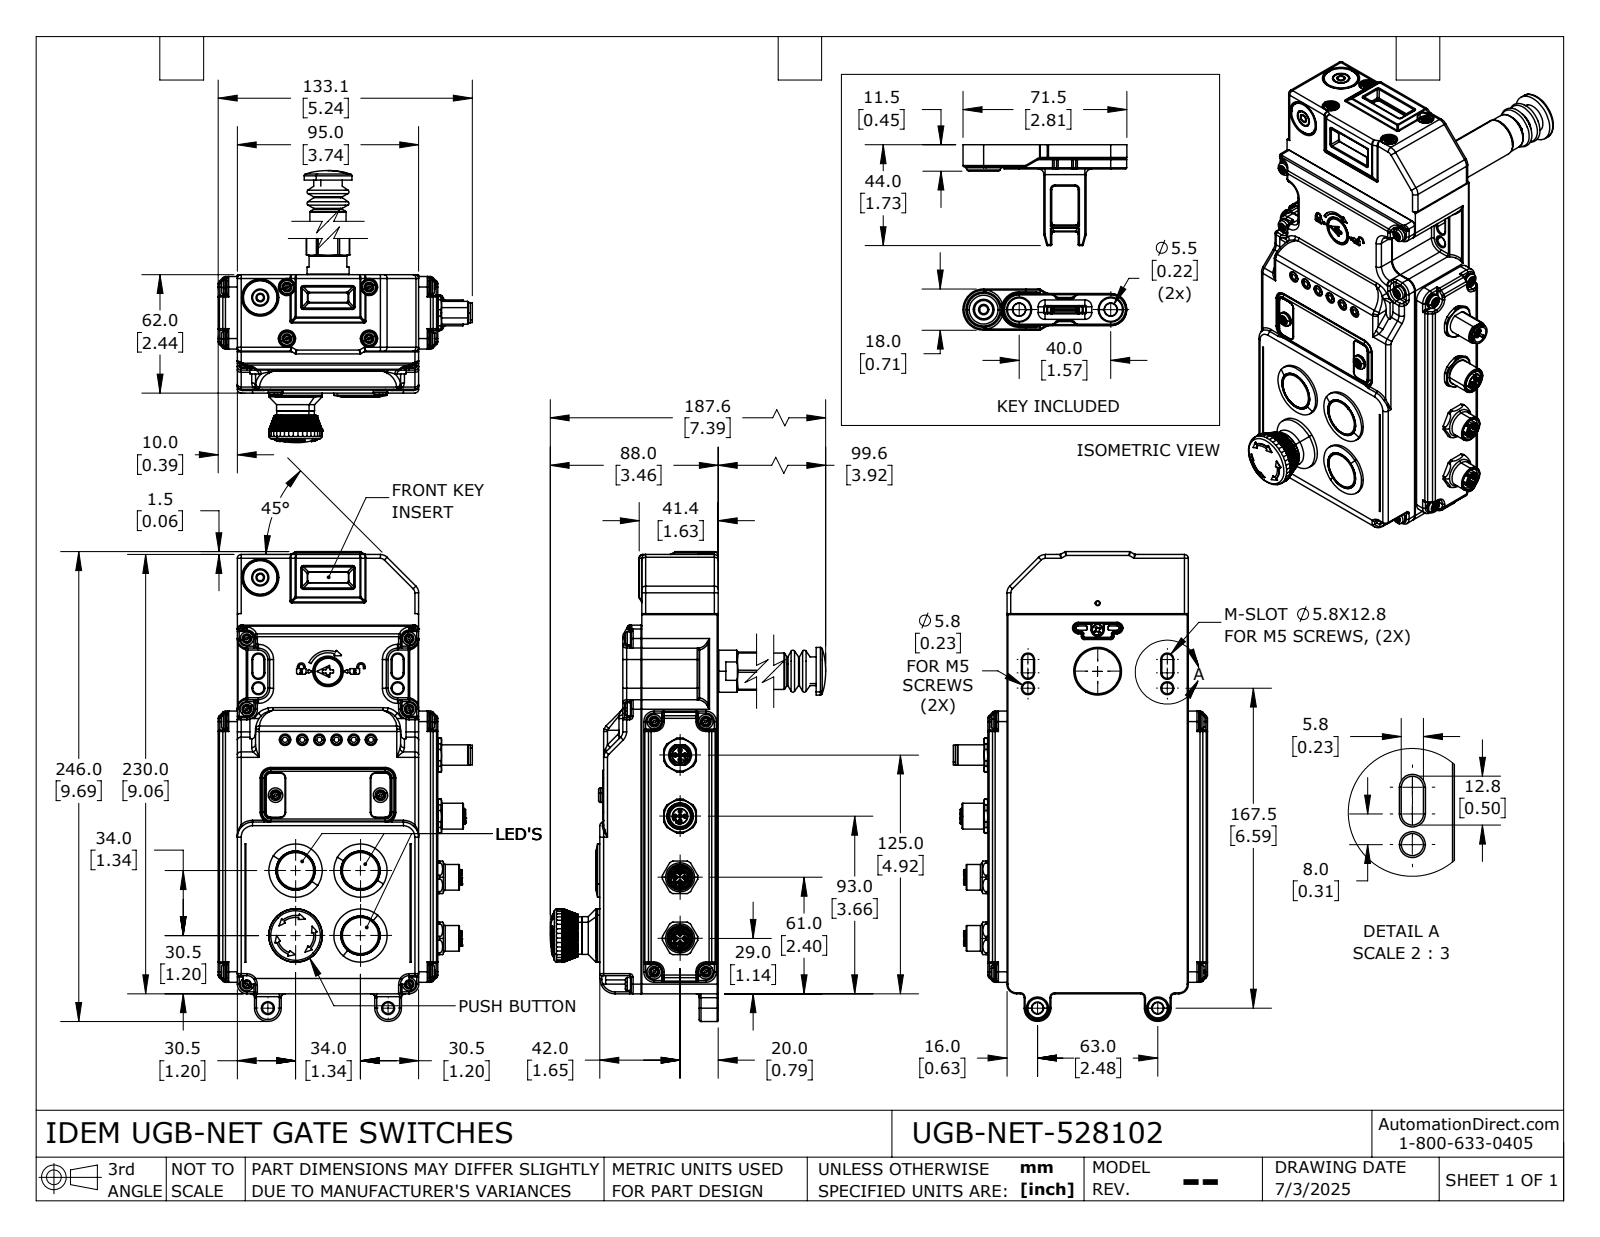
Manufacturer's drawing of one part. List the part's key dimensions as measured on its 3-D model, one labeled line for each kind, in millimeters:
Part name (STEP PRODUCT): UGB-NET-528102
STEP written by: SolidWorks 2024 (AUTOMOTIVE_DESIGN)
Units: millimetres
Bodies: 5 solids, 4648 faces (1396 planar, 1669 cylindrical, 1583 other)
Overall size (bounding box): 259.5 × 187.6 × 133.1
Volume: 1 324 000 mm³ · Surface area: 127 514 mm²
Round holes (diameter × count): ⌀4.5 ×14, ⌀2.5 ×9, ⌀1.25 ×8, ⌀1.95 ×8, ⌀8 ×8, ⌀2.2 ×7, ⌀4 ×6, ⌀5 ×6, ⌀1.1 ×5, ⌀5.8 ×4, ⌀20.05 ×3, ⌀3.3 ×2
Round bosses / shafts (diameter × count): ⌀1.3 ×16, ⌀7 ×8, ⌀4.8 ×8, ⌀3.5 ×8, ⌀1 ×7, ⌀7.6 ×6, ⌀2 ×5, ⌀6.5 ×4
Partial cylindrical surfaces — rounded edges, fillets, slot ends (radius × count): R1 ×233, R0.5 ×199, R2 ×72, R0.2 ×57, R0.8 ×47, R0.3 ×44, R0.4 ×14, R2.5 ×14
Main face-to-face distances: 10, 105, 62, 12, 2, 39, 95, 1.5, 1, 40
Hole centre spacings: 2.5, 3.54, 5, 27, 32.1, 32, 64, 64.05
